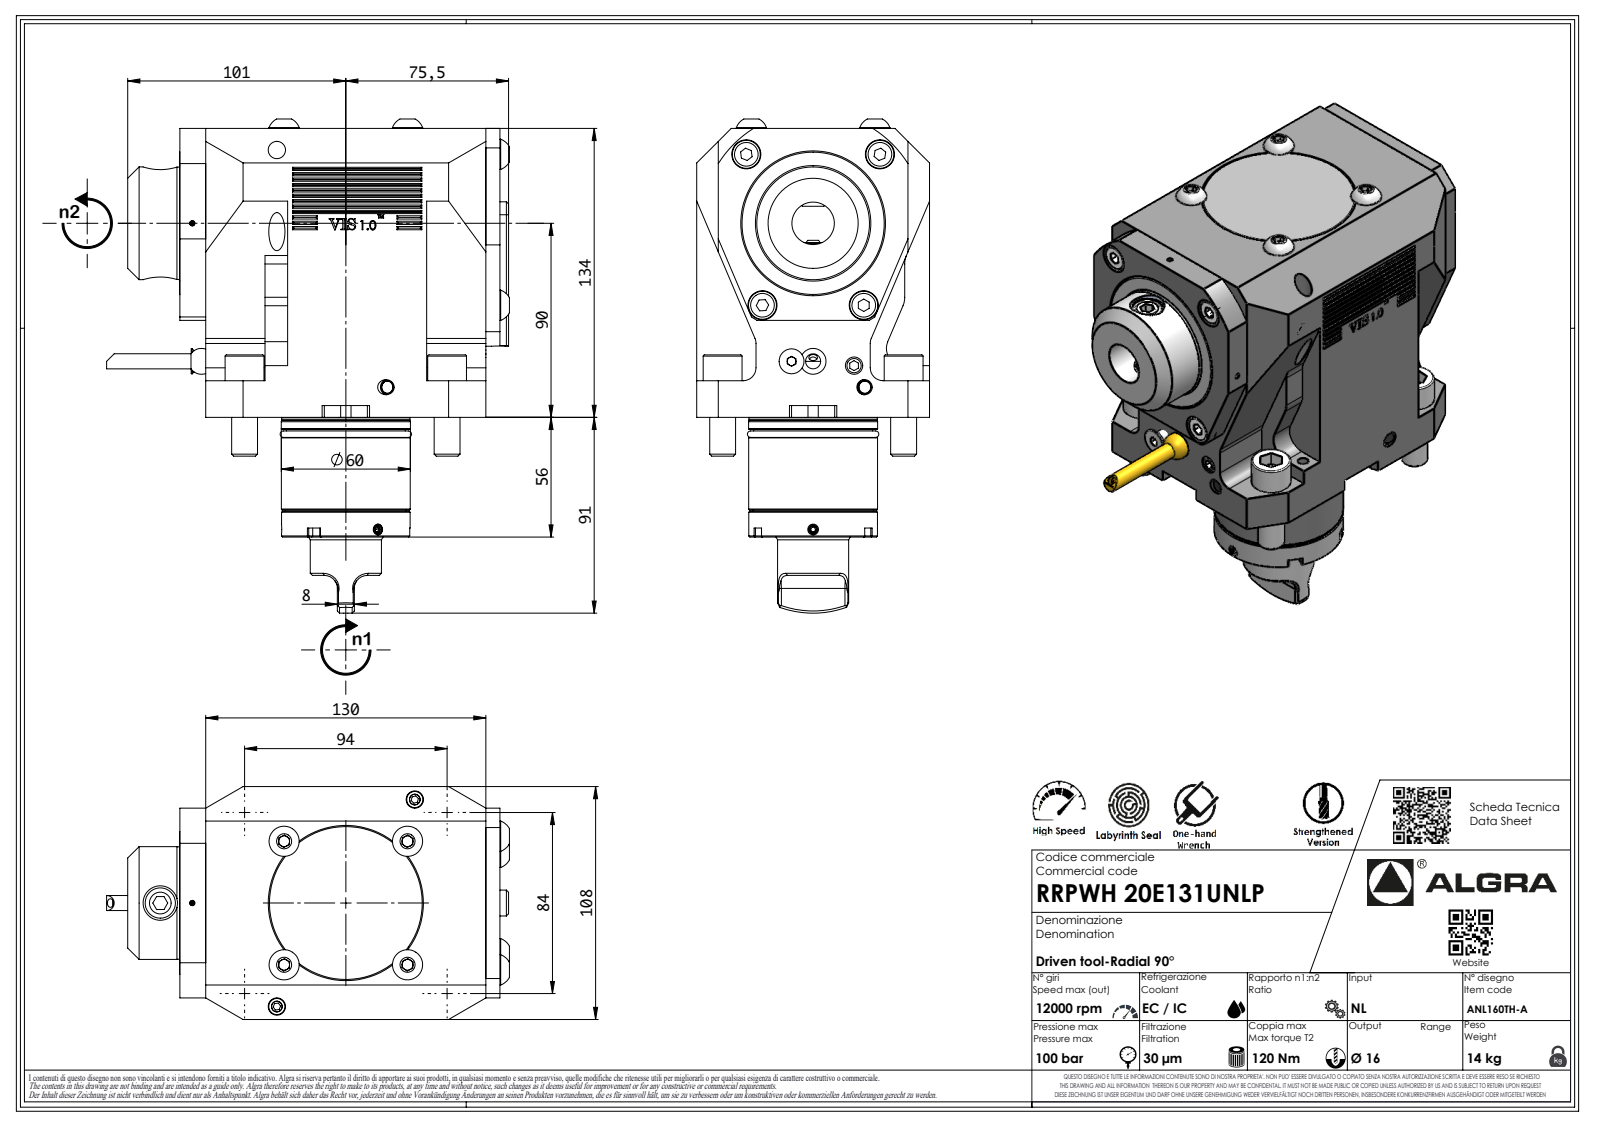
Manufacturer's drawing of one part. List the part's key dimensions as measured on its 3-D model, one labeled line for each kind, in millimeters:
Part name (STEP PRODUCT): RRPWH20E131UNLP
STEP written by: SolidWorks 2023 (AUTOMOTIVE_DESIGN)
Units: millimetres
Bodies: 1 solid, 931 faces (637 planar, 113 cylindrical, 181 other)
Overall size (bounding box): 224.8 × 186.5 × 108
Volume: 2 030 000 mm³ · Surface area: 125 706 mm²
Round holes (diameter × count): ⌀2.1 ×1, ⌀4 ×1
Round bosses / shafts (diameter × count): ⌀18 ×4, ⌀12 ×4, ⌀59.9 ×1, ⌀59.8 ×1, ⌀59.7 ×1, ⌀59.5 ×1, ⌀55.2 ×1, ⌀52.3 ×1
Partial cylindrical surfaces — rounded edges, fillets, slot ends (radius × count): R0.2 ×21, R8 ×18, R6 ×11, R0.33 ×7, R0.52 ×7, R3.7 ×7, R10 ×4, R3 ×3
Main face-to-face distances: 134, 108, 12, 27.5, 102.5, 148.5, 6.5, 136.5, 38, 5.5
